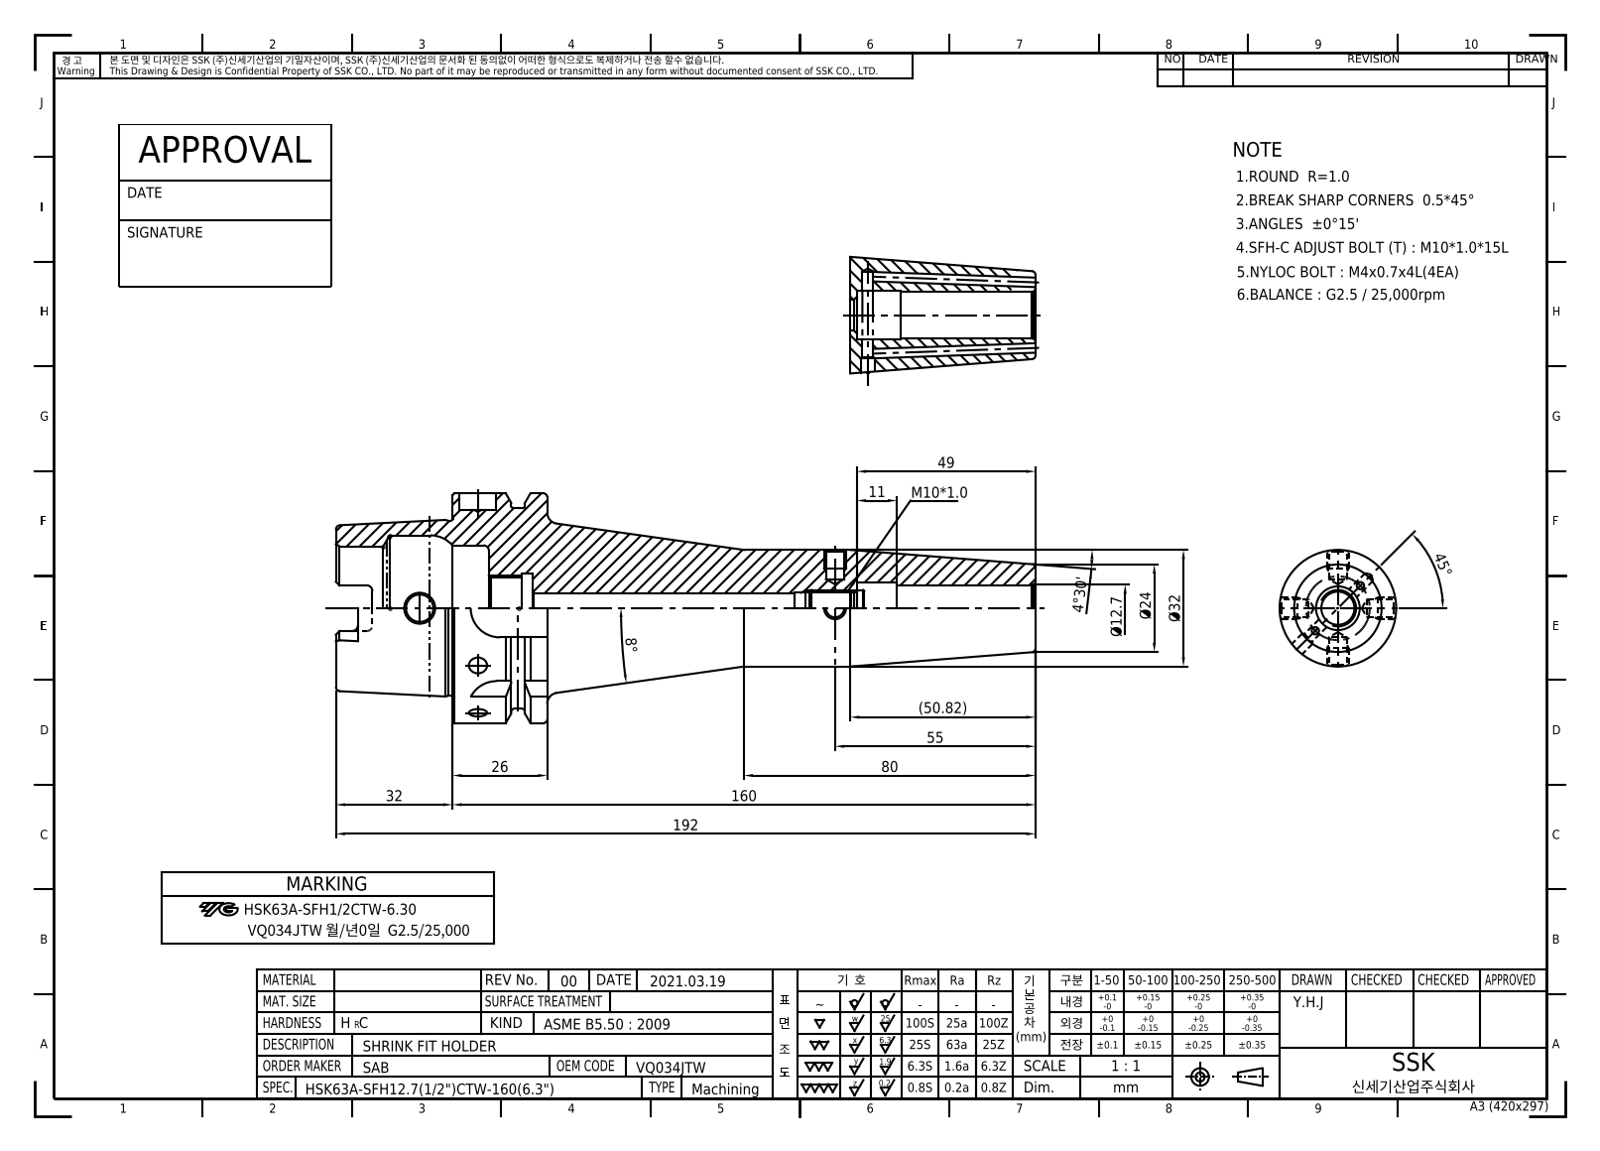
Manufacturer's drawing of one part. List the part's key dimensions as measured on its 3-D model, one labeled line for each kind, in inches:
Part name (STEP PRODUCT): HSK63A_BALANCE_20200217
STEP written by: CREO PARAMETRIC BY PTC INC, 2018500 (CONFIG_CONTROL_DESIGN)
Units: inches
Bodies: 1 solid, 186 faces (57 planar, 57 cylindrical, 72 other)
Overall size (bounding box): 7.559 × 2.48 × 2.48
Volume: 11.68 in³ · Surface area: 63.37 in²
Round holes (diameter × count): ⌀0.197 ×2, ⌀0.295 ×1, ⌀0.331 ×1, ⌀0.394 ×1, ⌀0.433 ×1, ⌀0.472 ×1, ⌀0.5 ×1, ⌀0.547 ×1, ⌀0.669 ×1, ⌀0.709 ×1, ⌀0.748 ×1, ⌀1.339 ×1
Round bosses / shafts (diameter × count): ⌀2.48 ×1, ⌀2.165 ×1, ⌀1.891 ×1, ⌀1.26 ×1
Partial cylindrical surfaces — rounded edges, fillets, slot ends (radius × count): R0.059 ×6, R0.113 ×4, R0.315 ×4
Main face-to-face distances: 1.024, 0.394, 0.63, 1.26, 0.241, 0.389, 1.654, 2.283, 0.157, 2.087
